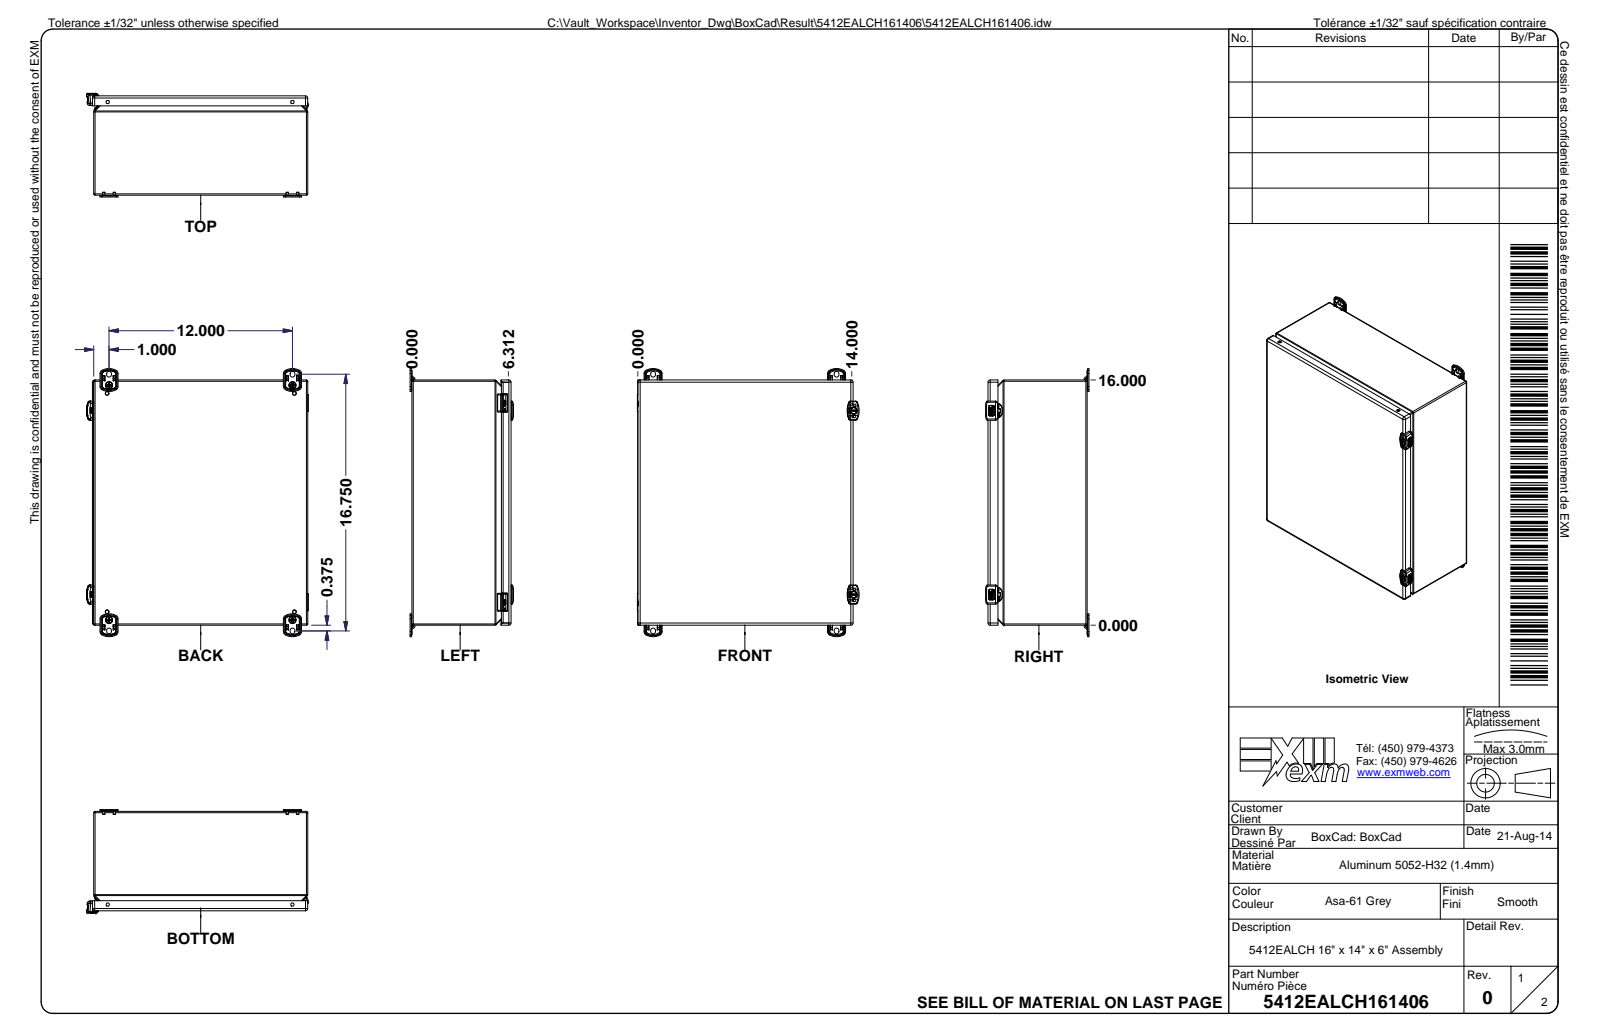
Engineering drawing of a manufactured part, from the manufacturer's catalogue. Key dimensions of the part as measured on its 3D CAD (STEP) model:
Part name (STEP PRODUCT): 5412EALCH161406; 5412EALCH161406B; 5412EALCH161406B-P; RIVET_NUT_SS_M6_FH_CE (+8 more)
STEP written by: Autodesk Inventor 2024 (AUTOMOTIVE_DESIGN)
Units: inches
Bodies: 53 solids, 7363 faces (3255 planar, 1768 cylindrical, 2340 other)
Overall size (bounding box): 17.496 × 14.441 × 6.756
Volume: 64.21 in³ · Surface area: 2 279 in²
Round holes (diameter × count): ⌀0.197 ×4, ⌀0.197 ×4, ⌀0.236 ×4, ⌀0.32 ×4, ⌀0.03 ×2, ⌀0.165 ×2, ⌀0.173 ×2, ⌀0.175 ×2, ⌀0.201 ×2, ⌀0.218 ×2, ⌀0.23 ×2, ⌀0.236 ×2
Round bosses / shafts (diameter × count): ⌀0.232 ×8, ⌀0.5 ×4, ⌀0.236 ×4, ⌀0.197 ×3, ⌀0.412 ×2, ⌀0.394 ×2, ⌀0.33 ×2, ⌀0.3 ×2
Partial cylindrical surfaces — rounded edges, fillets, slot ends (radius × count): R0.008 ×224, R0.02 ×188, R0.01 ×100, R0.004 ×97, R0.039 ×89, R0.059 ×59, R0.031 ×33, R0.012 ×28
Main face-to-face distances: 0.053, 6.429, 6.376, 6.482, 6.125, 0.236, 0.304, 0.357, 6.072, 0.289
Hole centre spacings: 19.118, 0.546, 12.137, 14.781, 13, 12, 12.25, 12.25
